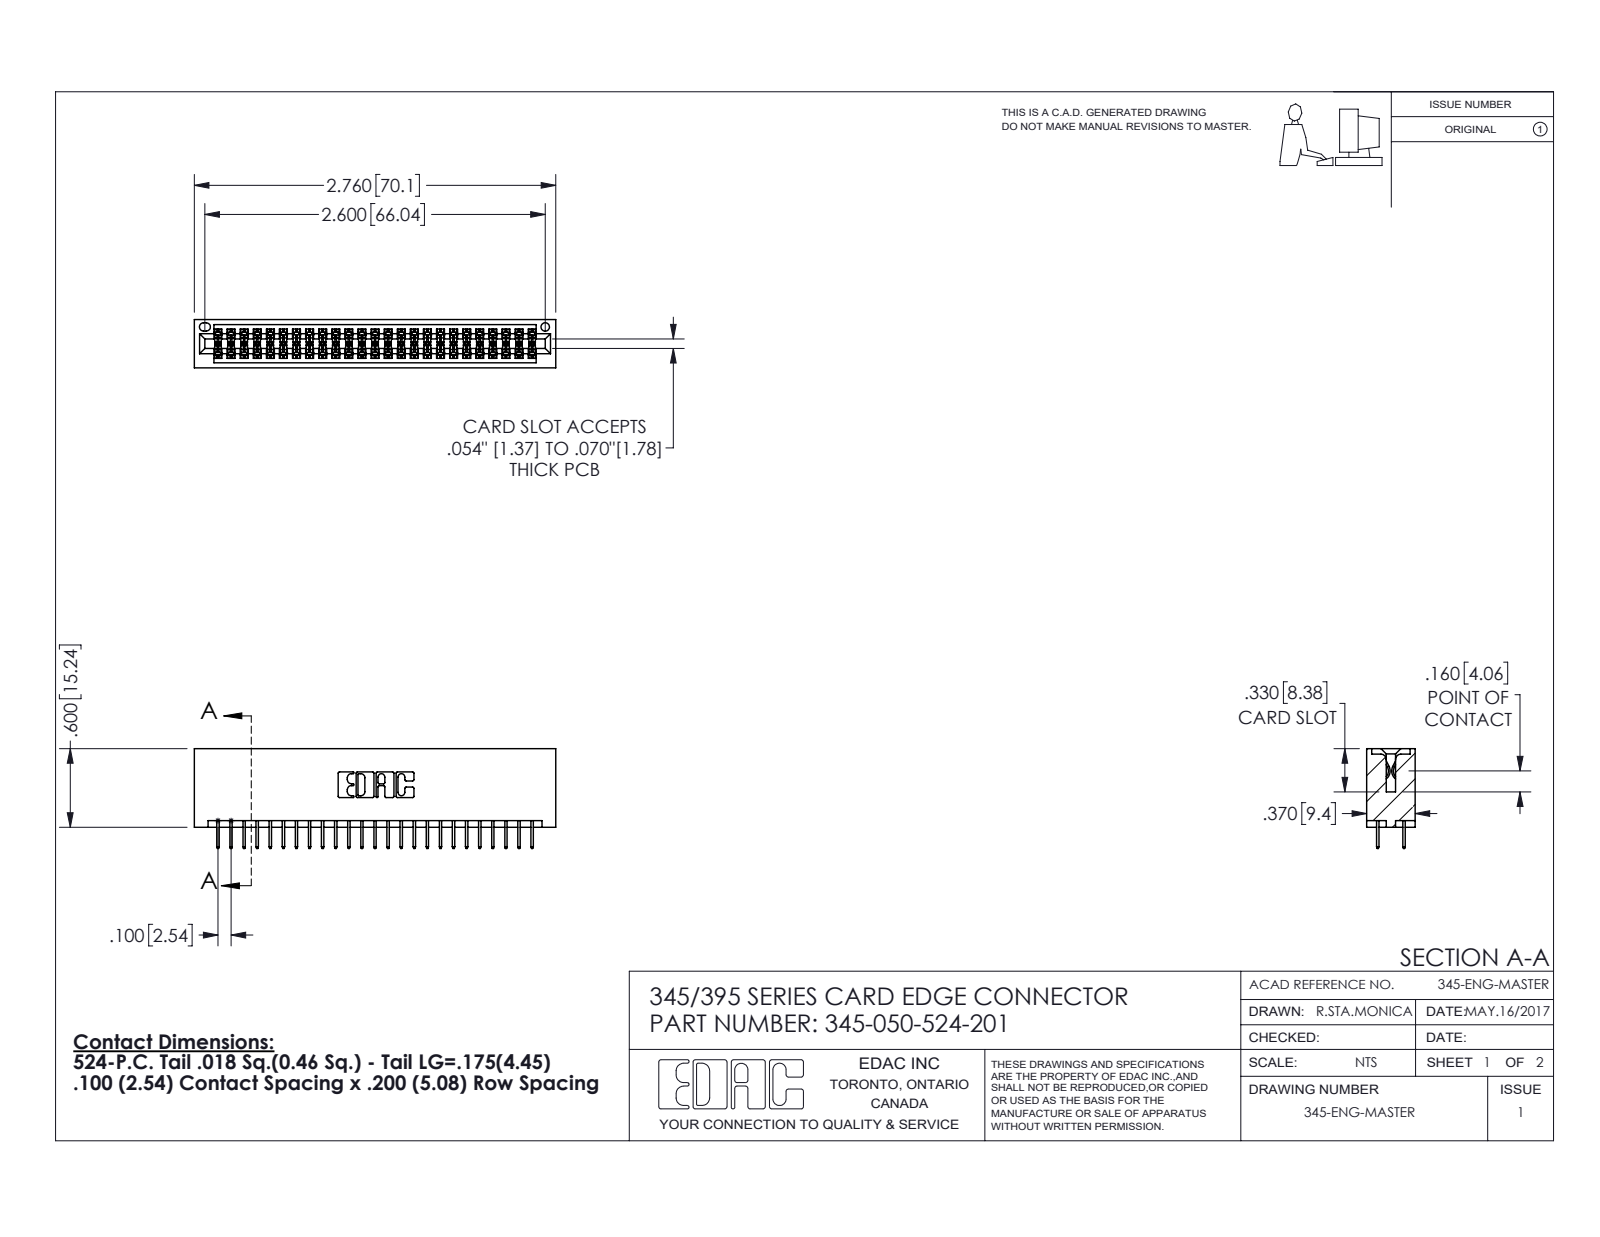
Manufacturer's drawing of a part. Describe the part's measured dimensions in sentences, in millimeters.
The part is named "345-050-524-201; 345 Part_No Mounting Lugs; 345-292-001_345-293-124". Its 3-D file was written by "SolidWorks 2016 (CONFIG_CONTROL_DESIGN)". It is 51 solids with 2818 faces: 2026 planar, 792 cylindrical and 0 other. Overall it measures 70.1 by 19.4 by 9.4 millimeters. Its volume is 7 190 cubic millimeters and its surface area 10 410 square millimeters. Round holes: 1 of diameter 1.6. Partial cylindrical surfaces (rounded edges, fillets, slot ends): 75 of radius 0.2, 22 of radius 0.3, 6 of radius 0.2, 6 of radius 0.8, 3 of radius 0.7, 2 of radius 0.4, 2 of radius 0.5, 2 of radius 0.6. The main face-to-face distances are 7.6, 1.8, 5.1, 9.4, 2.5, 6.9, 0.6, 5.7, 1.8, 4.4.
